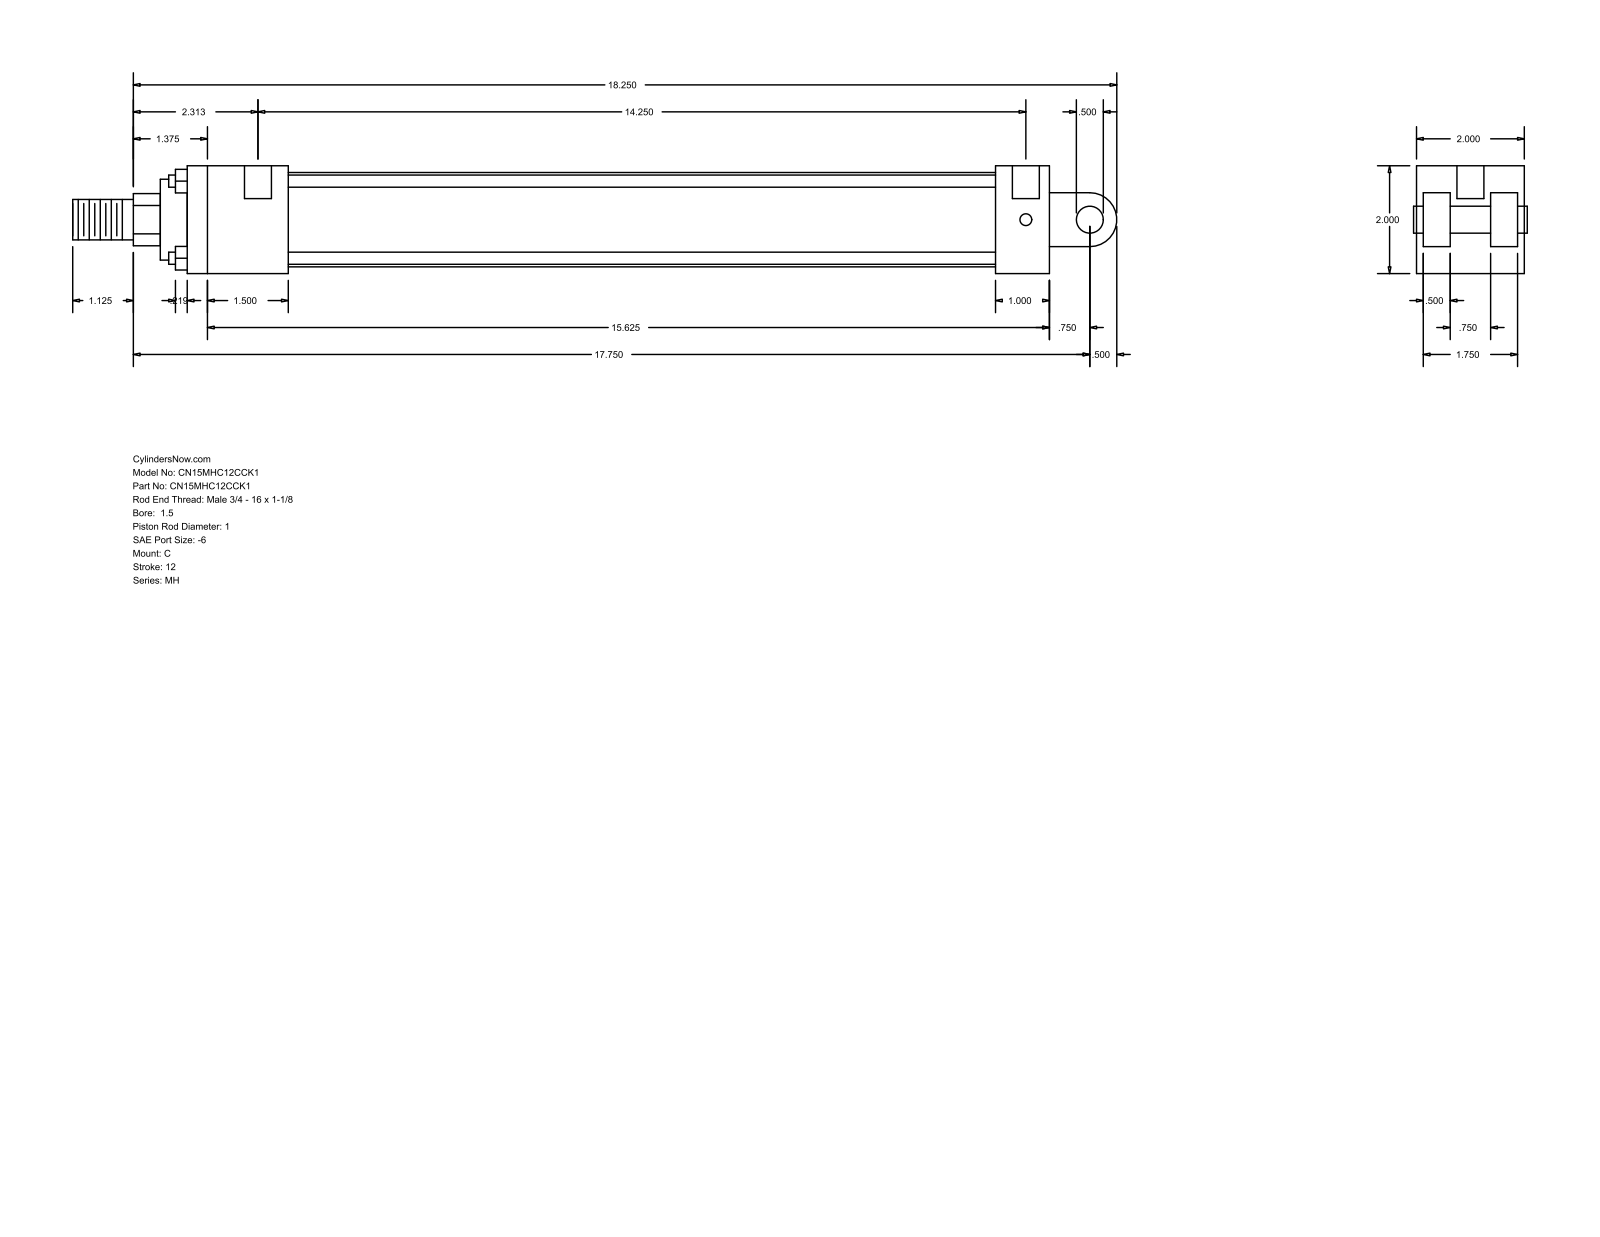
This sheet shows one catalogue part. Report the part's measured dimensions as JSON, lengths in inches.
{"part_name": "MH_C__0150_1", "step_written_by": "GSSL Pune (CONFIG_CONTROL_DESIGN)", "units": "inches", "bodies": {"solids": 0, "faces": 99, "planar": 70, "cylindrical": 29, "other": 0}, "overall_size": [19.375, 2, 2], "round_holes": [[0.219, 4], [0.5, 2]], "round_bosses_or_shafts": [[0.225, 4], [1.75, 1], [1.5, 1], [1, 1], [0.75, 1], [0.5, 1]], "partial_cylinders_radius": [[0.484, 1], [0.5, 1]], "face_to_face_distances": [2, 0.5, 1.875, 1, 0.125, 0.625, 1.375, 1.25, 16, 1.5], "hole_center_spacings": [14.375, 0.125, 14.25]}
